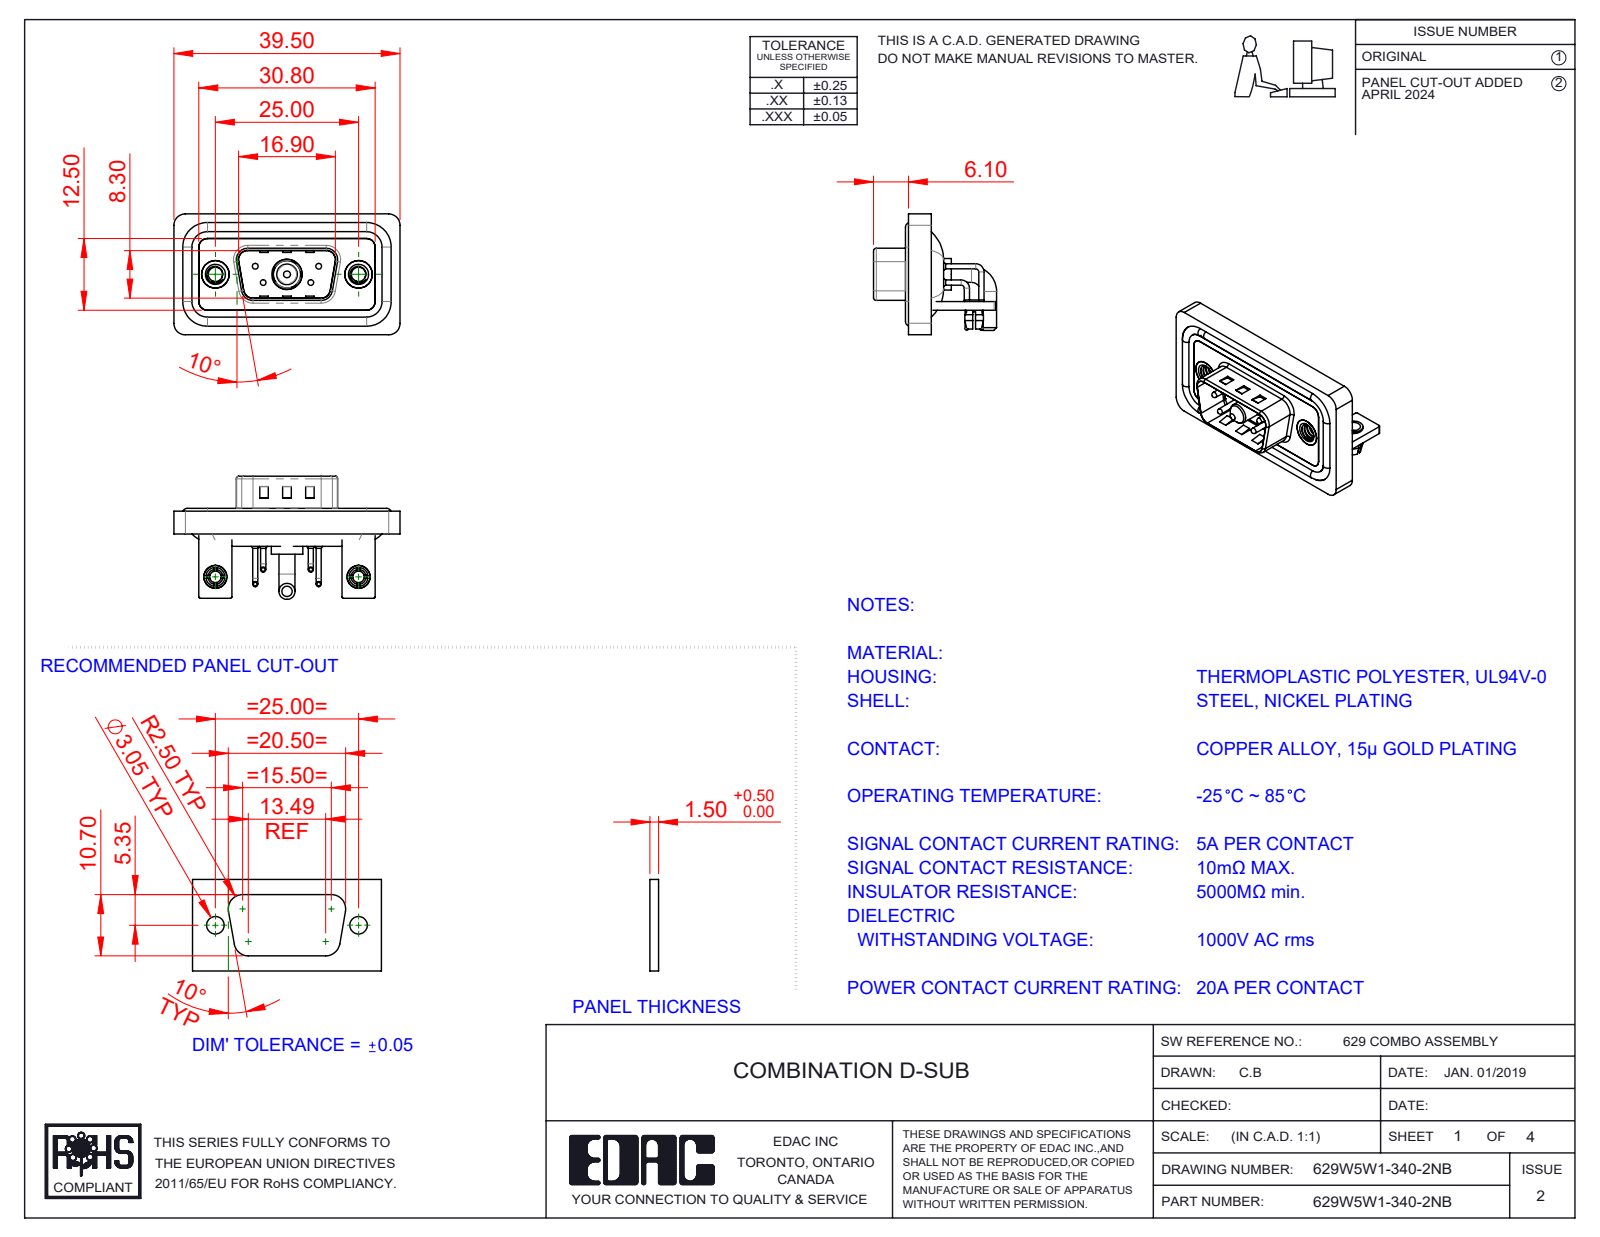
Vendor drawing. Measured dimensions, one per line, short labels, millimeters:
name: 629Combo Shell Rear_09 Contacts; 629Combo Shell Front_09 Contacts; 629Combo Threaded Rivet_B; 629Combo Housing_5W1 (+7 more)
written by: SolidWorks 2023 (CONFIG_CONTROL_DESIGN)
unit: mm
bodies: 17 solids, 1024 faces (479 planar, 395 cylindrical, 150 other)
size: 39.5 × 21.5 × 21.1
volume: 4 784 mm³; area: 7 962 mm²
holes: 6× ⌀2, 4× ⌀0.75, 4× ⌀1.6, 4× ⌀2.5, 2× ⌀3.2, 2× ⌀4, 2× ⌀4.8, 2× ⌀5, 1× ⌀4.85, 1× ⌀5.3
bosses: 8× ⌀0.9, 4× ⌀1.6, 4× ⌀1.5, 4× ⌀1, 4× ⌀0.65, 2× ⌀4.9, 2× ⌀4, 2× ⌀3.4
rounds: 19× R2, 18× R1.5, 16× R0.25, 9× R0.5, 8× R1.6, 4× R0.6, 4× R0.65, 4× R0.9
face distances: 0.4, 1.5, 0.8, 2.9, 1.1, 2.1, 1.2, 1.6, 2.5, 3.7
hole spacings: 3.16, 5.72, 7.1, 12.5, 18.1, 25, 4.39, 4.4
